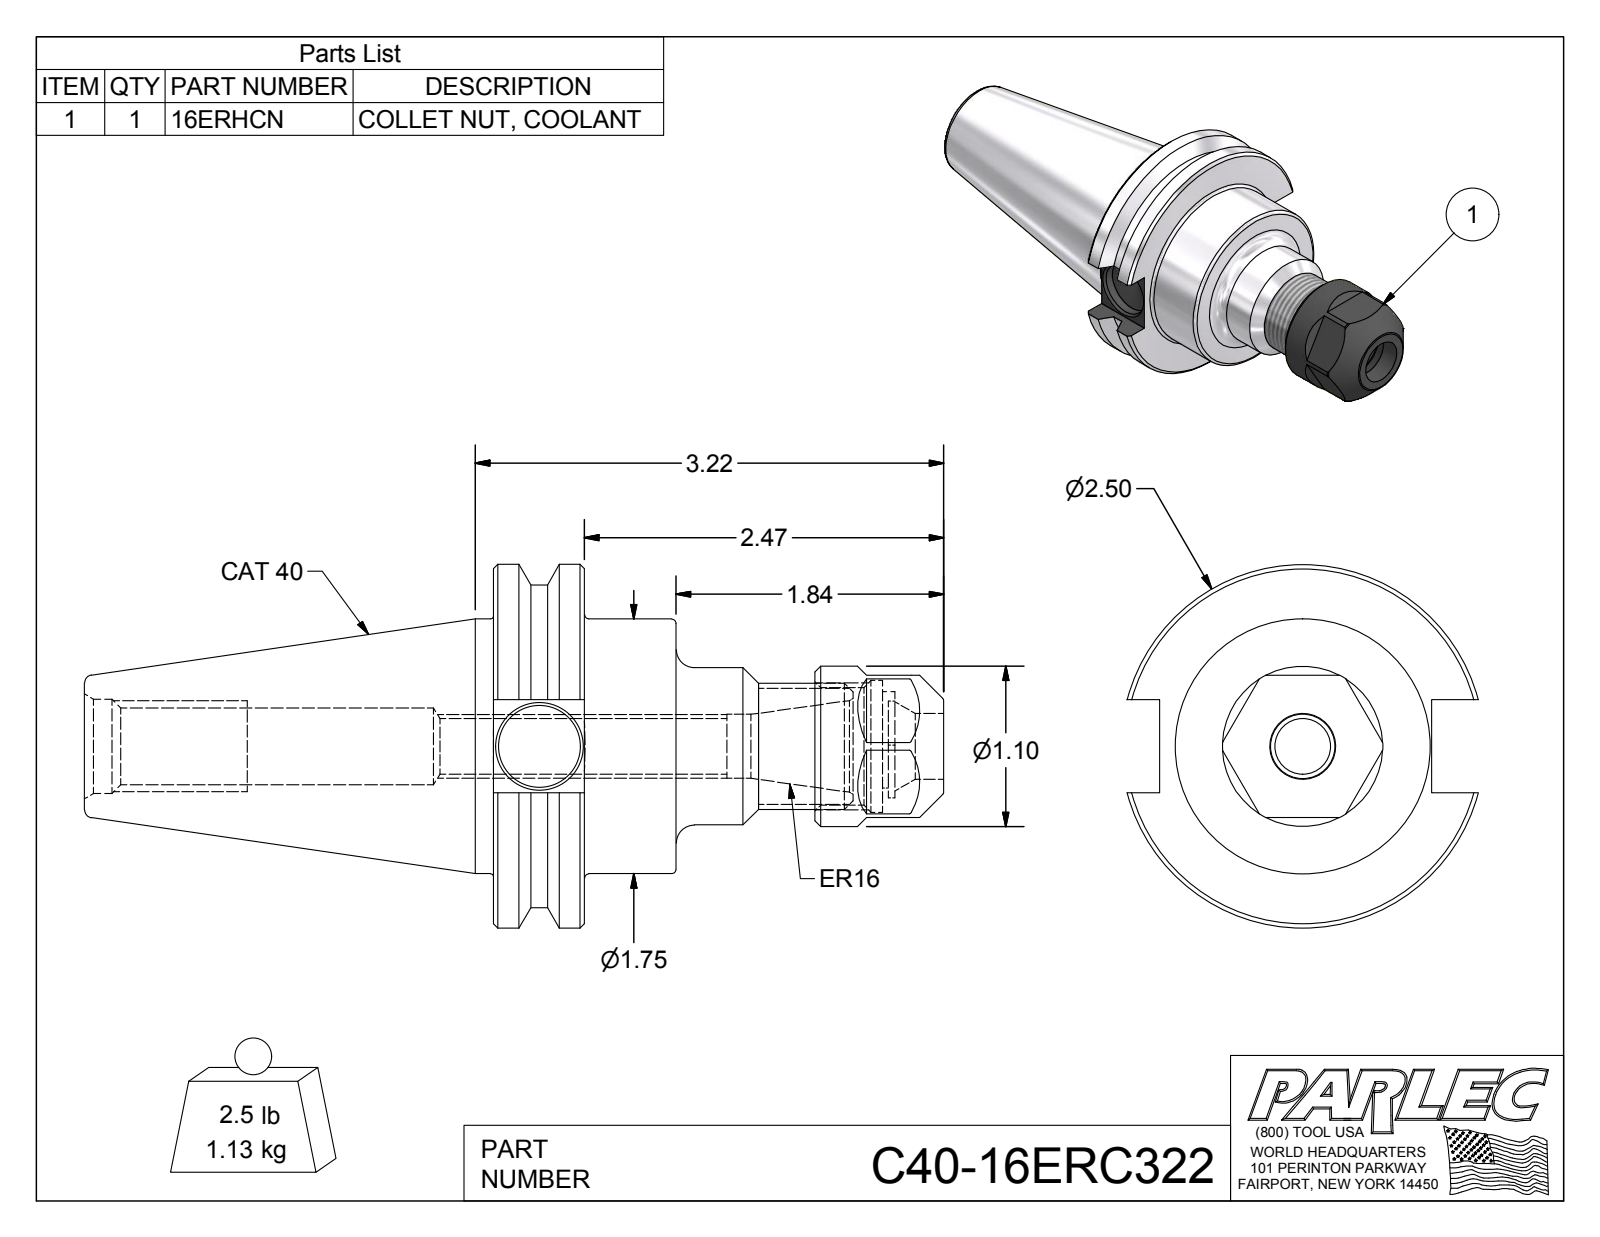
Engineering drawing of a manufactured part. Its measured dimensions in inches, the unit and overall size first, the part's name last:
Units: inches
Overall size (bounding box): 5.907 × 2.5 × 2.417
Round holes (diameter × count): ⌀0.315 ×1, ⌀0.383 ×1, ⌀0.399 ×1, ⌀0.44 ×1, ⌀0.453 ×1, ⌀0.527 ×1, ⌀0.648 ×1, ⌀0.661 ×1, ⌀0.807 ×1, ⌀0.906 ×1
Round bosses / shafts (diameter × count): ⌀2.5 ×1, ⌀2.219 ×1, ⌀1.75 ×1, ⌀1.102 ×1, ⌀1.08 ×1, ⌀0.866 ×1
Partial cylindrical surfaces — rounded edges, fillets, slot ends (radius × count): R0.354 ×1
Main face-to-face distances: 0.625, 1.255, 0.63, 0.979, 0.169, 0.809, 2.674, 2.049, 1.419, 0.64
Hole centre spacings: 0.051
Volume: 8.721 in³ · Surface area: 45.89 in²
Bodies: 2 solids, 87 faces (30 planar, 22 cylindrical, 35 other)
Part name (STEP PRODUCT): C40-16ER3-1; 16ERHCN; C40-16ERC322
STEP written by: Autodesk Inventor 2016 (AUTOMOTIVE_DESIGN)
